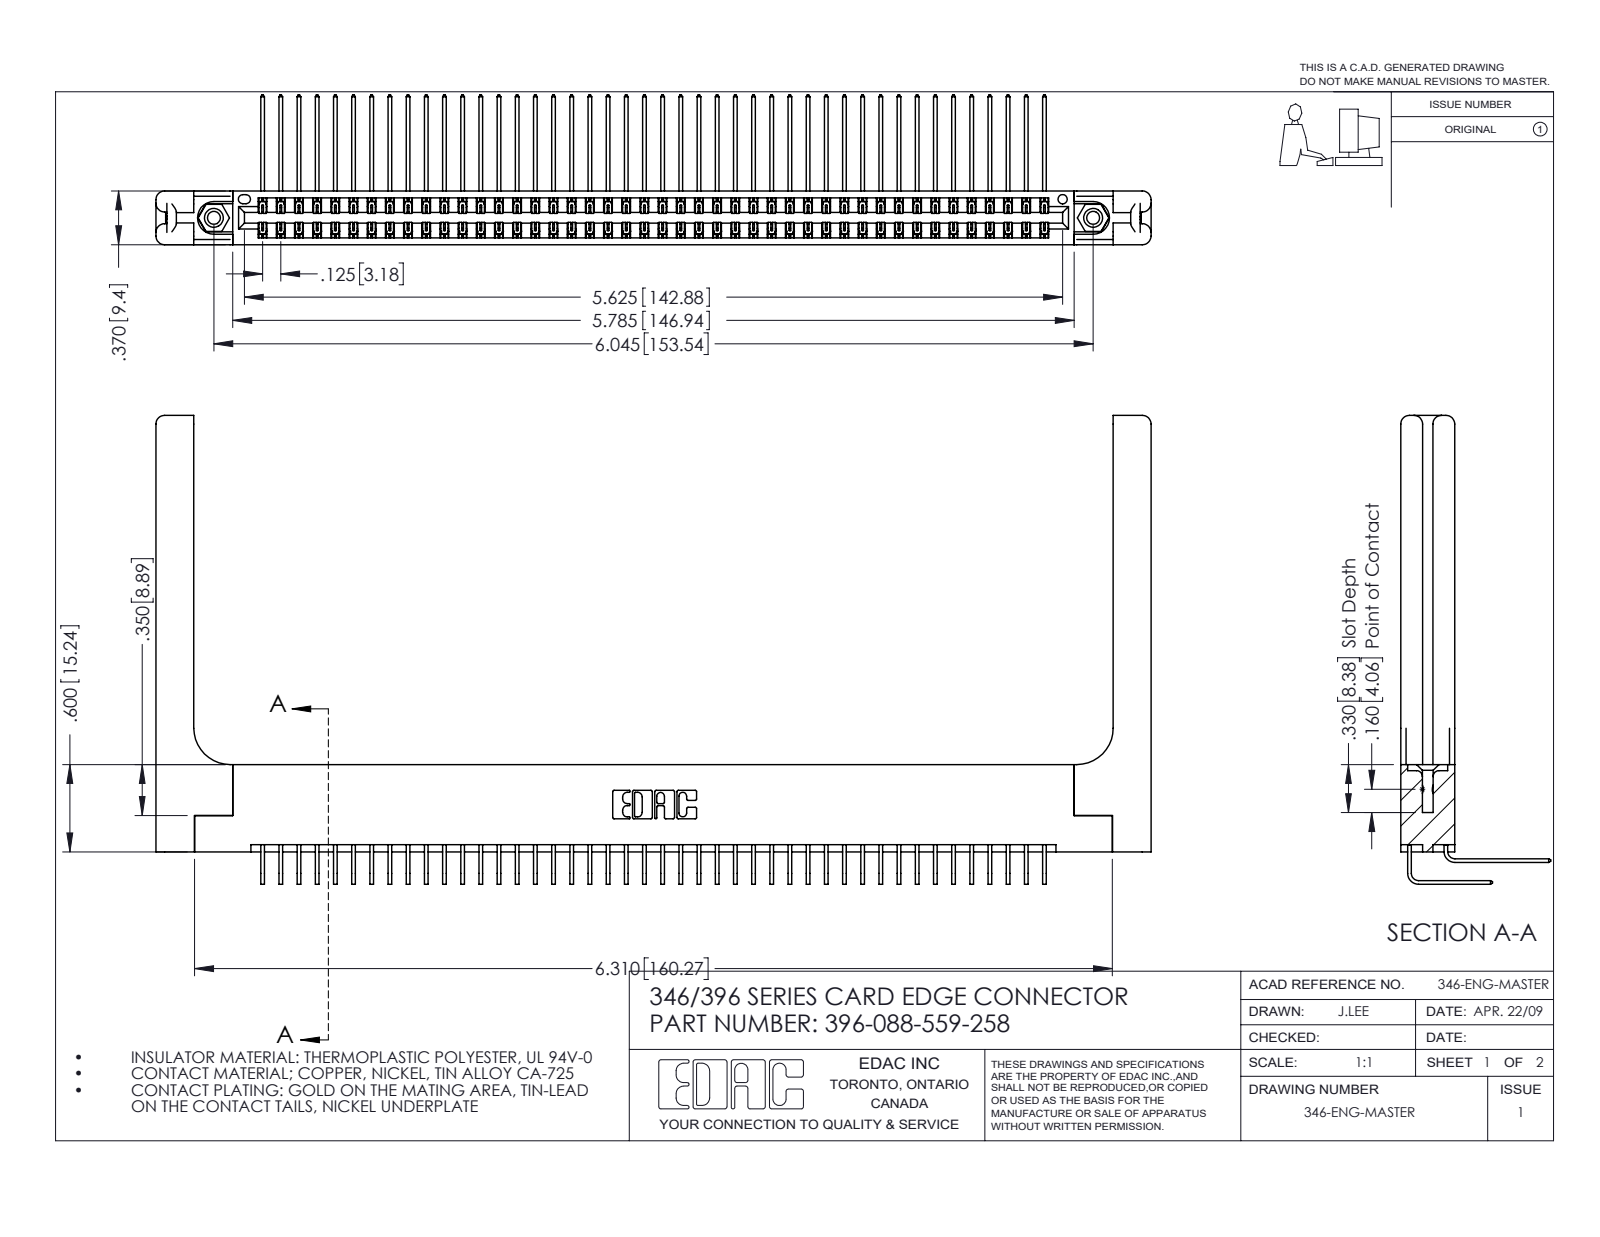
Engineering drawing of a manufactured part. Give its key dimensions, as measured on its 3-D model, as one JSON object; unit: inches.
{"part_name": "396-088-559-258; 345-250-001_345-250-001-102; 345-292-001_558 559 Tail - 1; 346-220-058_345-220-058 (+2 more)", "step_written_by": "SolidWorks 2016 (CONFIG_CONTROL_DESIGN)", "units": "inches", "bodies": {"solids": 93, "faces": 5130, "planar": 3480, "cylindrical": 1590, "other": 60}, "overall_size": [6.841, 3.223, 1.03], "volume_in3": 1.523, "surface_area_in2": 48.75, "round_holes": [[0.089, 2], [0.125, 2], [0.156, 2], [0.064, 1]], "round_bosses_or_shafts": [[0.155, 2]], "partial_cylinders_radius": [[0.006, 132], [0.01, 22], [0.06, 16], [0.007, 6], [0.031, 6], [0.026, 3], [0.014, 2], [0.022, 2]], "face_to_face_distances": [0.048, 0.322, 0.37, 0.072, 0.025, 0.148, 0.15, 0.25, 0.298, 0.275], "hole_center_spacings": [0.246, 5.836, 6.045]}
